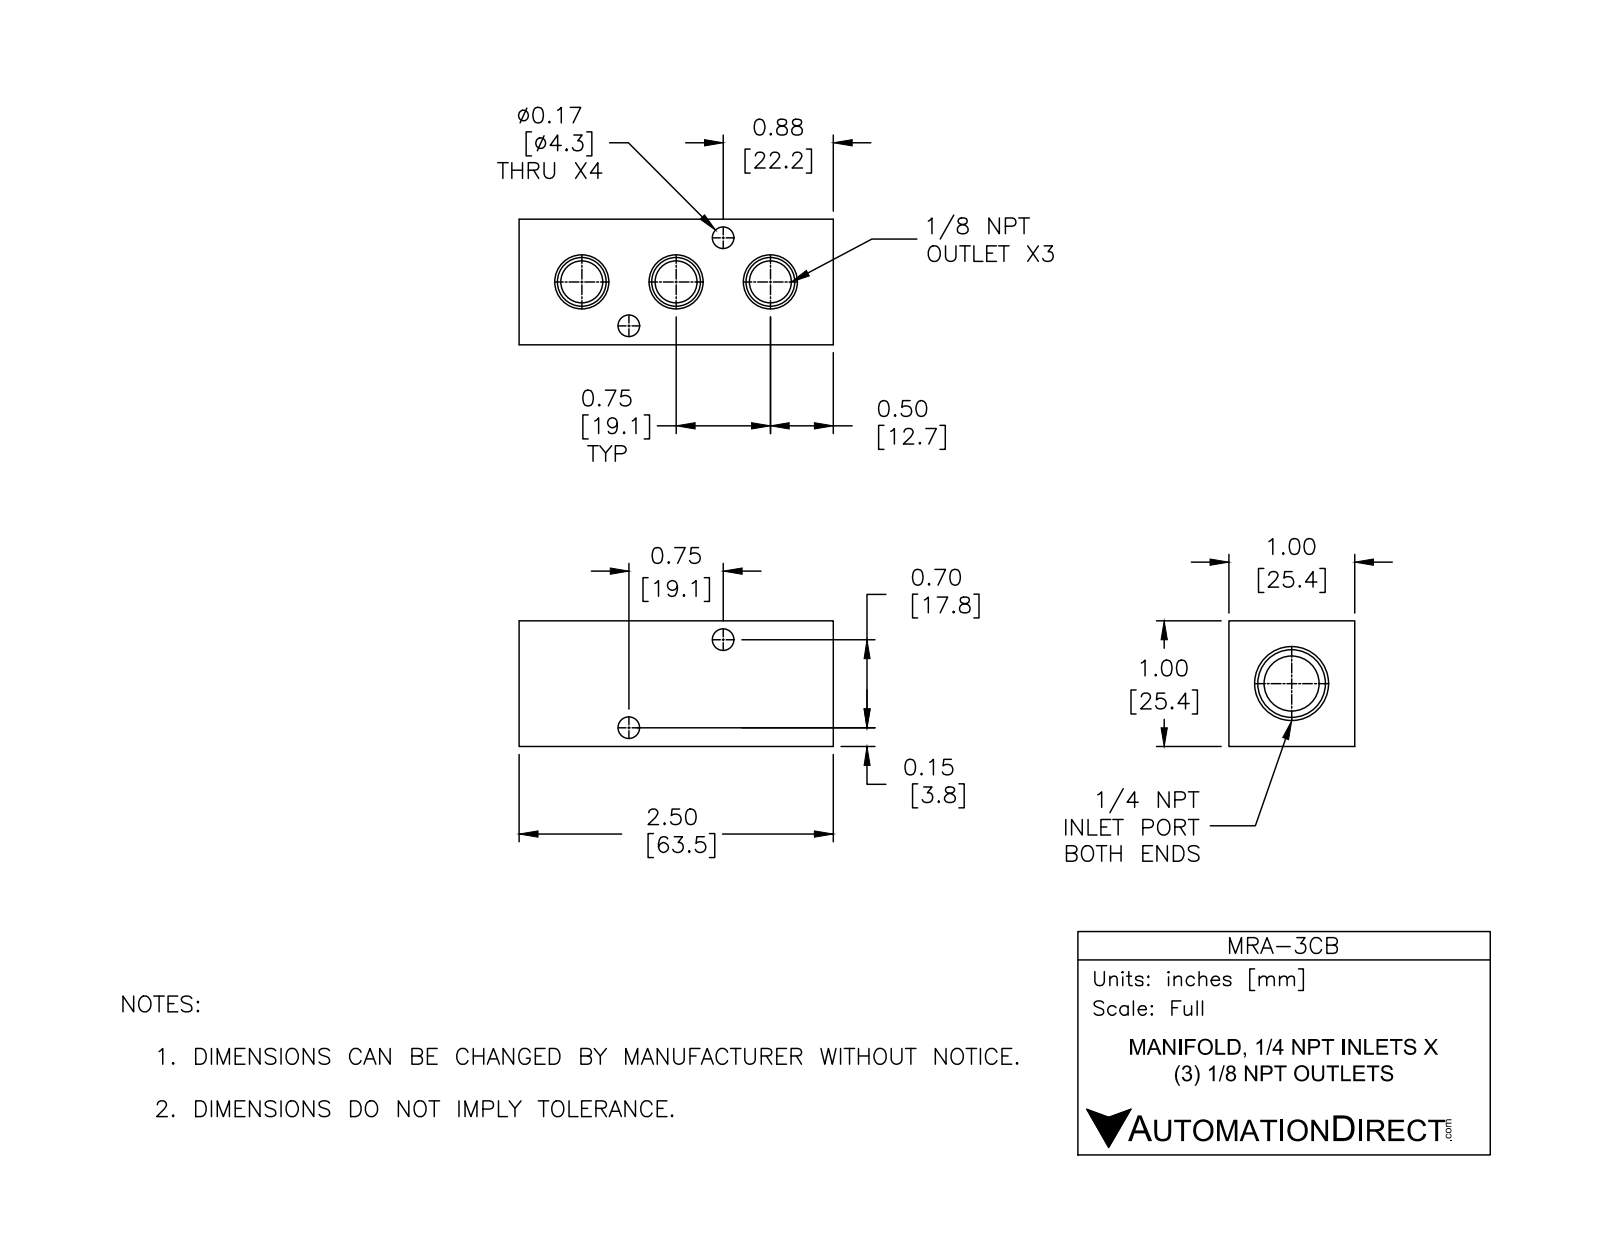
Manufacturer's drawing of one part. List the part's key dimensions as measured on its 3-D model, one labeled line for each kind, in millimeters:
Part name (STEP PRODUCT): MRA-3CB
STEP written by: SolidWorks 2015 (CONFIG_CONTROL_DESIGN)
Units: millimetres
Bodies: 1 solid, 54 faces (11 planar, 23 cylindrical, 20 other)
Overall size (bounding box): 63.5 × 25.4 × 25.4
Volume: 30 760 mm³ · Surface area: 11 280 mm²
Round holes (diameter × count): ⌀4.3 ×4, ⌀8.4 ×1, ⌀11.1 ×1
Partial cylindrical surfaces — rounded edges, fillets, slot ends (radius × count): R4.2 ×2
Main face-to-face distances: 25.4, 63.5, 9.9, 53.6, 18.5, 6.9, 43.7
Hole centre spacings: 13, 26.1
